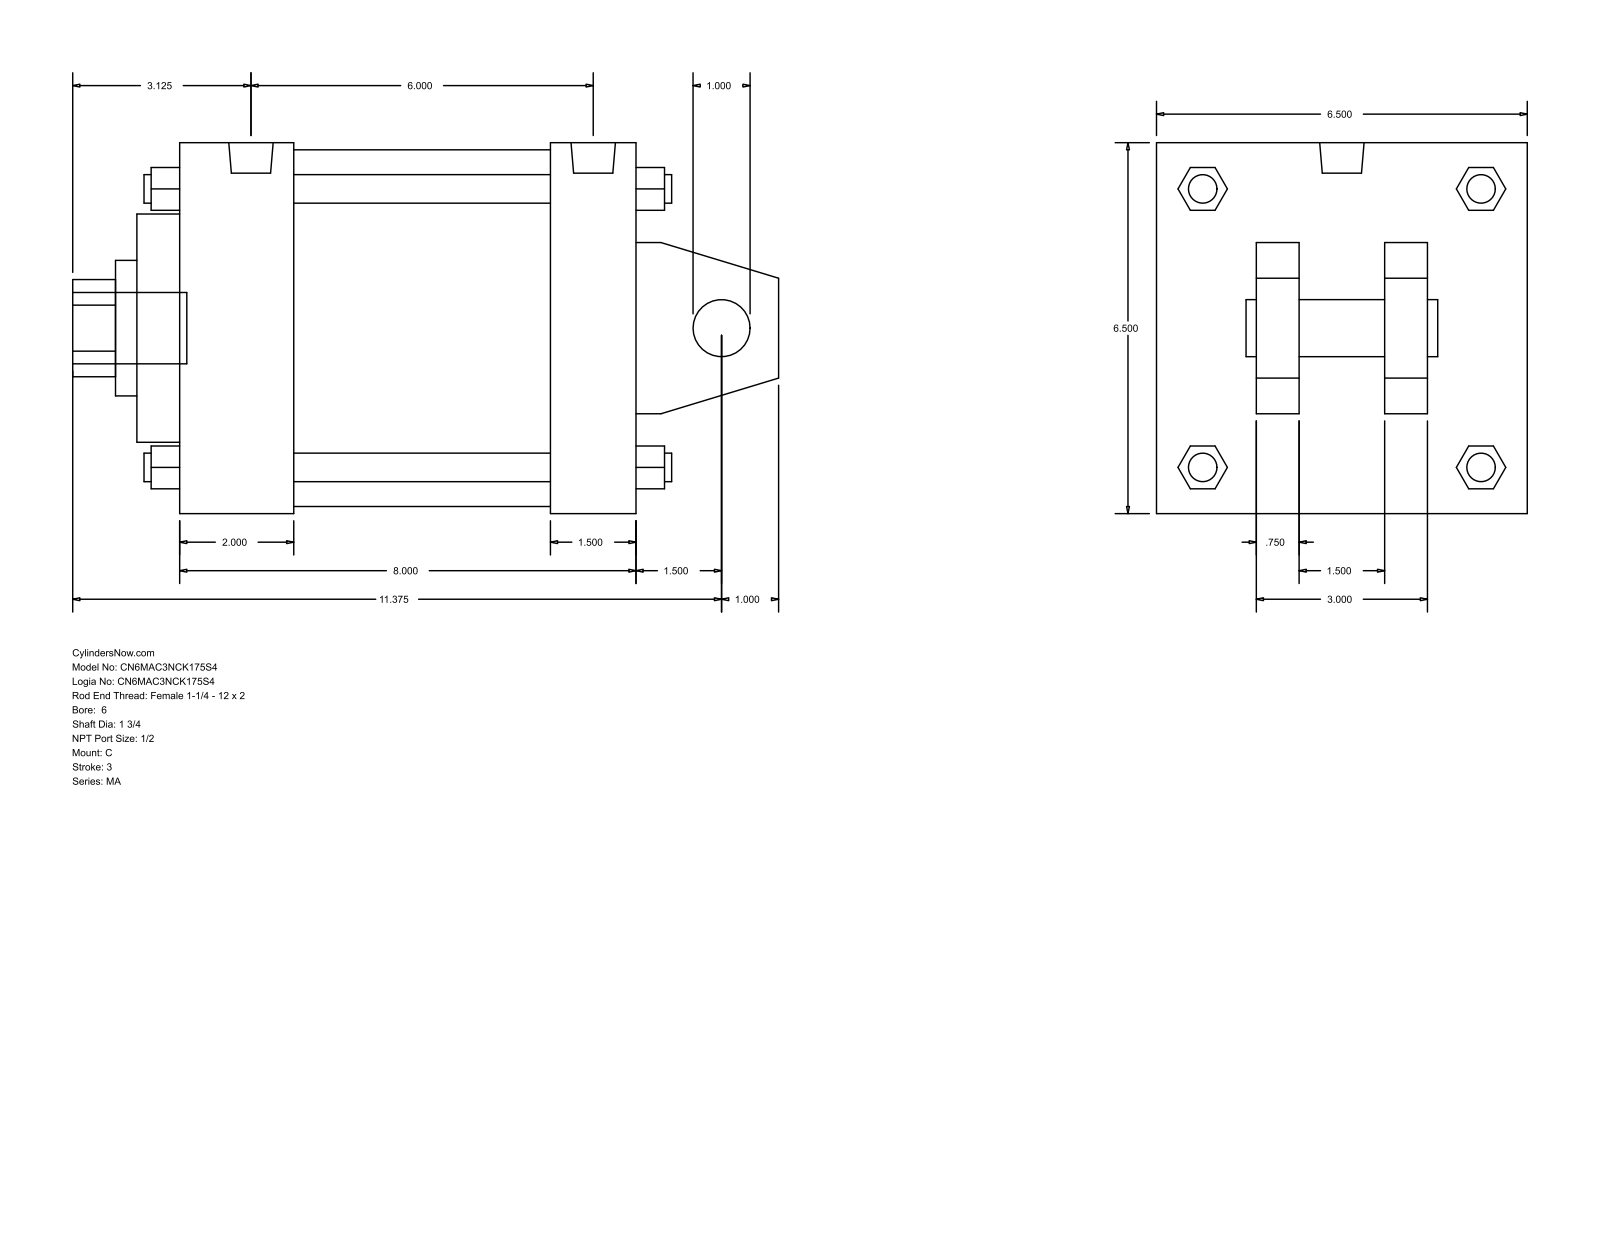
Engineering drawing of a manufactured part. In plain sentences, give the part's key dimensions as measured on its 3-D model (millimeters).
The part is named "MA_C__0600_1.75". Its 3-D file was written by "GSSL Pune (CONFIG_CONTROL_DESIGN)". It is 0 solids with 141 faces: 109 planar, 32 cylindrical and 0 other. Overall it measures 314.32 by 165.1 by 165.1 millimeters. Round holes: 1 of diameter 25.4, 1 of diameter 44.45, 1 of diameter 60.33, 1 of diameter 101.6, 1 of diameter 158.75. Round bosses or shafts: 4 of diameter 17.46, 4 of diameter 12.7, 2 of diameter 19.77, 1 of diameter 31.75. Partial cylindrical surfaces (rounded edges, fillets, slot ends): 1 of radius 21.63. The main face-to-face distances are 165.1, 203.2, 19.05, 38.1, 63.5, 101.6, 50.8, 120.65, 44.45, 57.15.
